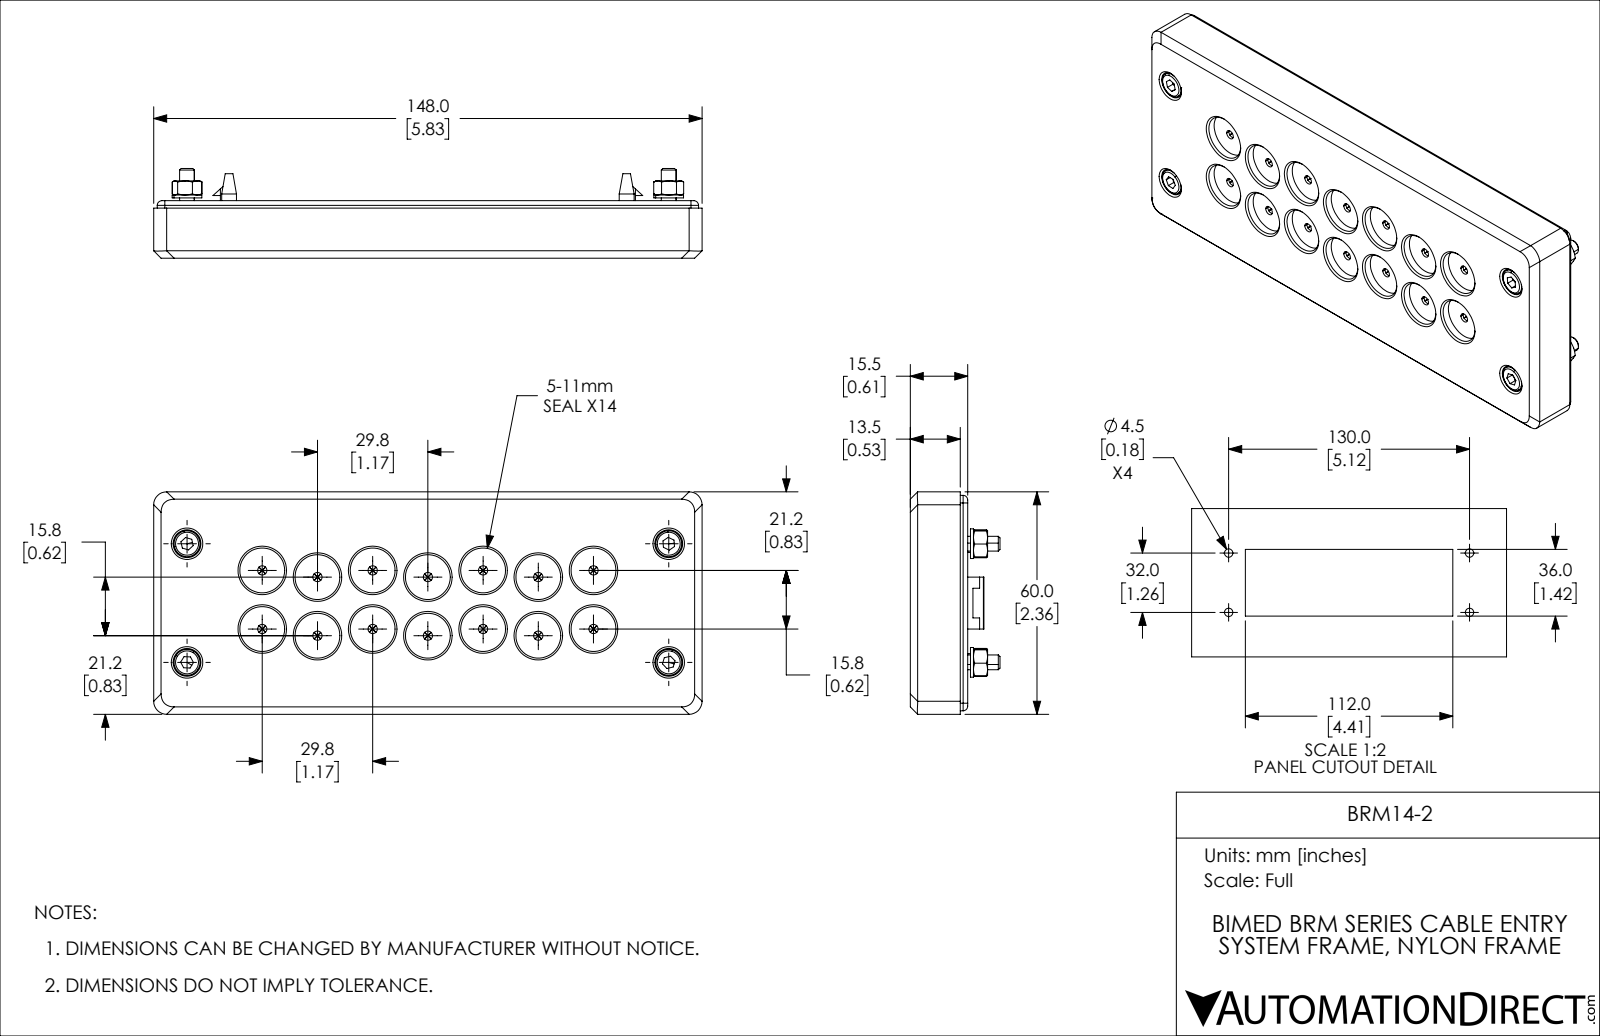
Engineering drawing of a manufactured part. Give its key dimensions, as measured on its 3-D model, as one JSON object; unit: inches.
{"part_name": "BRM14-2", "step_written_by": "SolidWorks 2021 (CONFIG_CONTROL_DESIGN)", "units": "inches", "bodies": {"solids": 18, "faces": 1231, "planar": 385, "cylindrical": 574, "other": 272}, "overall_size": [5.827, 2.362, 0.953], "volume_in3": 5.457, "surface_area_in2": 138.8, "round_holes": [[0.11, 21], [0.098, 18], [0.476, 14], [0.551, 14], [0.128, 4], [0.169, 4], [0.177, 4], [0.295, 4]], "round_bosses_or_shafts": [[0.098, 16], [0.157, 8], [0.315, 4], [0.276, 4]], "partial_cylinders_radius": [[0.039, 28], [0.049, 8], [0.197, 8], [0.02, 6], [0.079, 4], [0.081, 4], [0.138, 4], [0.195, 4]], "face_to_face_distances": [0.031, 0.079, 0.11, 0.118, 0.197, 0.228, 0.098, 0.13, 0.327, 0.209], "hole_center_spacings": [0.591, 1.173, 1.328, 1.761, 0.622, 0.805, 0.908, 2.346]}
